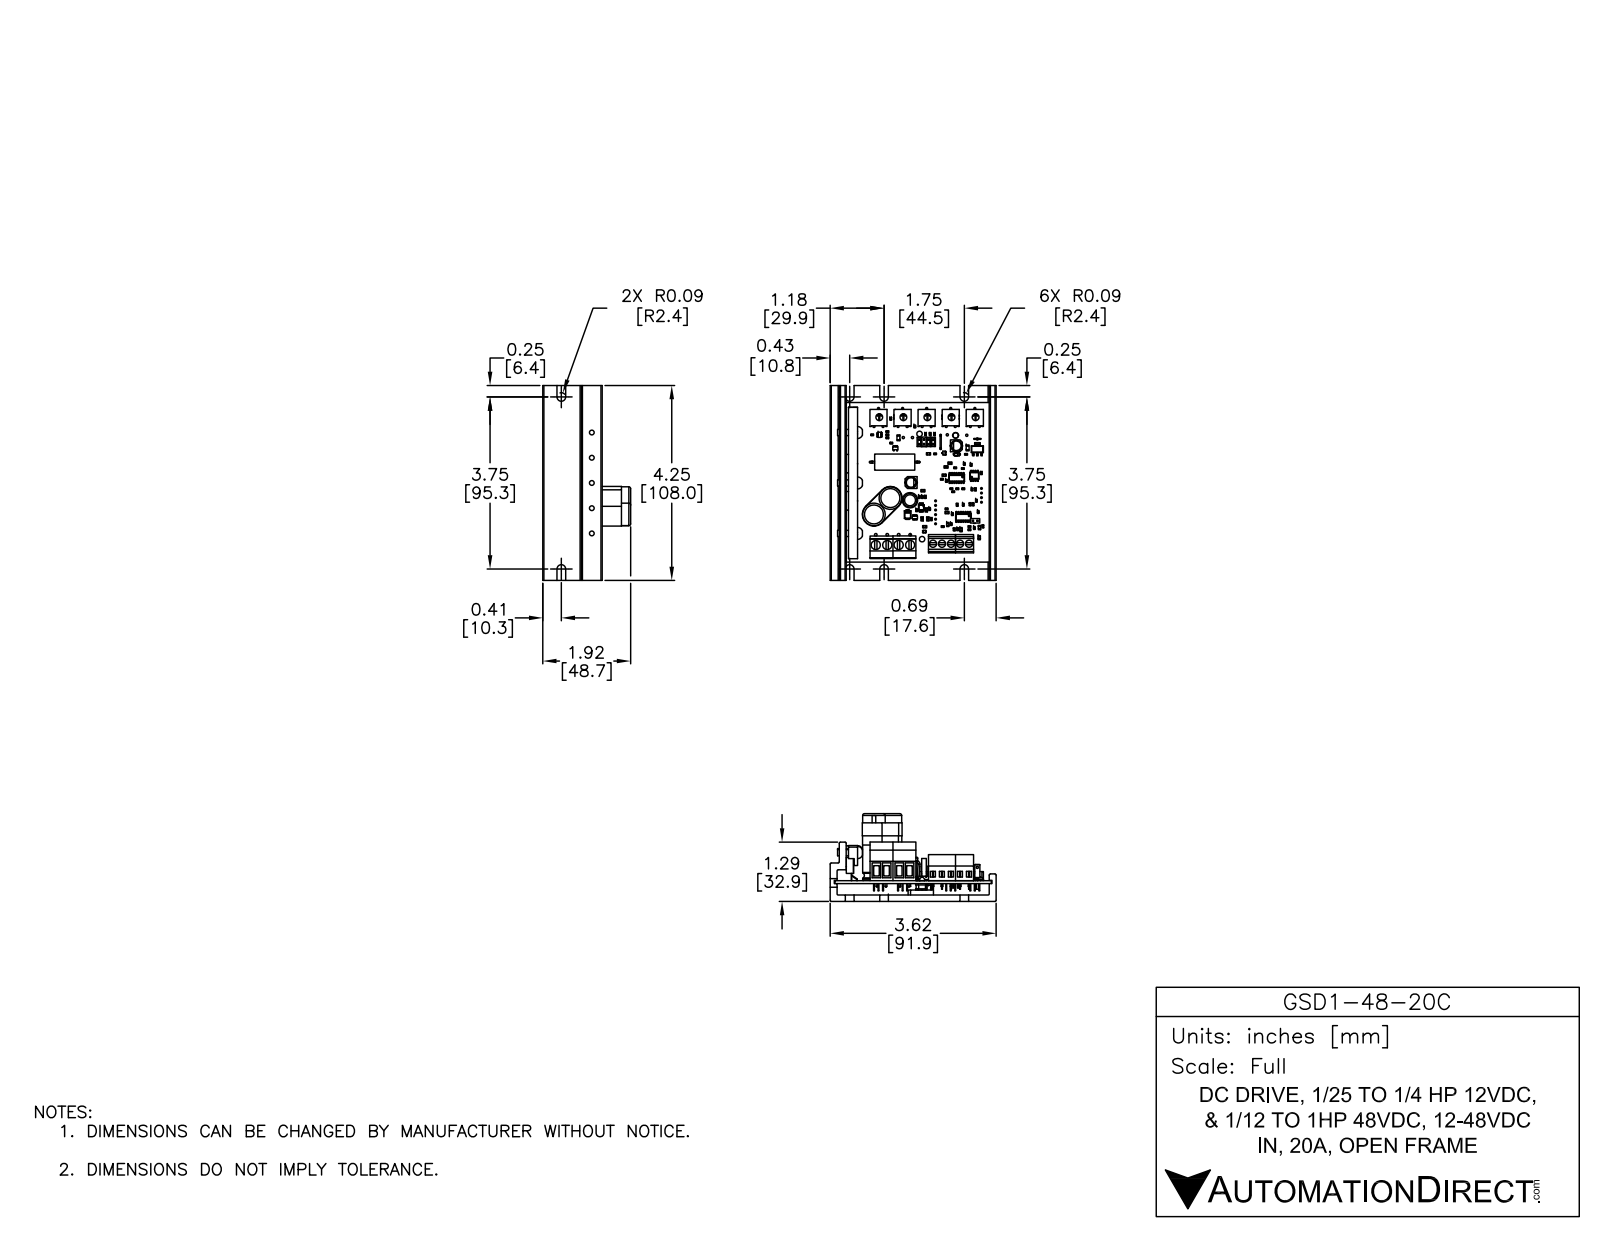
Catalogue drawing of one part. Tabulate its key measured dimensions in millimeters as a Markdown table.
| quantity | value |
| --- | --- |
| part name | GSD1-48-20C |
| STEP written by | SolidWorks 2015 (AUTOMOTIVE_DESIGN) |
| units | millimeters |
| bodies | 0 solids, 1163 faces (803 planar, 296 cylindrical, 64 other) |
| overall size | 107.95 × 91.95 × 48.77 |
| round holes (diameter × count) | 1.17 × 14, 1.02 × 10, 0.31 × 8, 1.09 × 6, 1.27 × 5, 3.78 × 5, 3.99 × 5, 0.84 × 4, 1.47 × 4, 5.08 × 4, 1.01 × 3, 2.64 × 2 |
| round bosses / shafts (diameter × count) | 0.63 × 6, 1.7 × 5, 3.42 × 3, 12.5 × 2, 6.3 × 2, 8.5 × 1, 7.54 × 1, 3.2 × 1 |
| partial cylindrical surfaces (radius × count) | 0.11 × 12, 0.64 × 11, 2.39 × 8, 0.13 × 3, 0.1 × 2, 0.3 × 2, 5.25 × 2, 6.33 × 2 |
| main face-to-face distances | 3.56, 6.35, 9.91, 11.48, 7.92, 1.57, 3.81, 5.08, 83.06, 88.14 |
| hole center spacings | 2.54, 5.08, 10.32, 7.62, 26.67, 13.34, 26.31, 27.08 |
